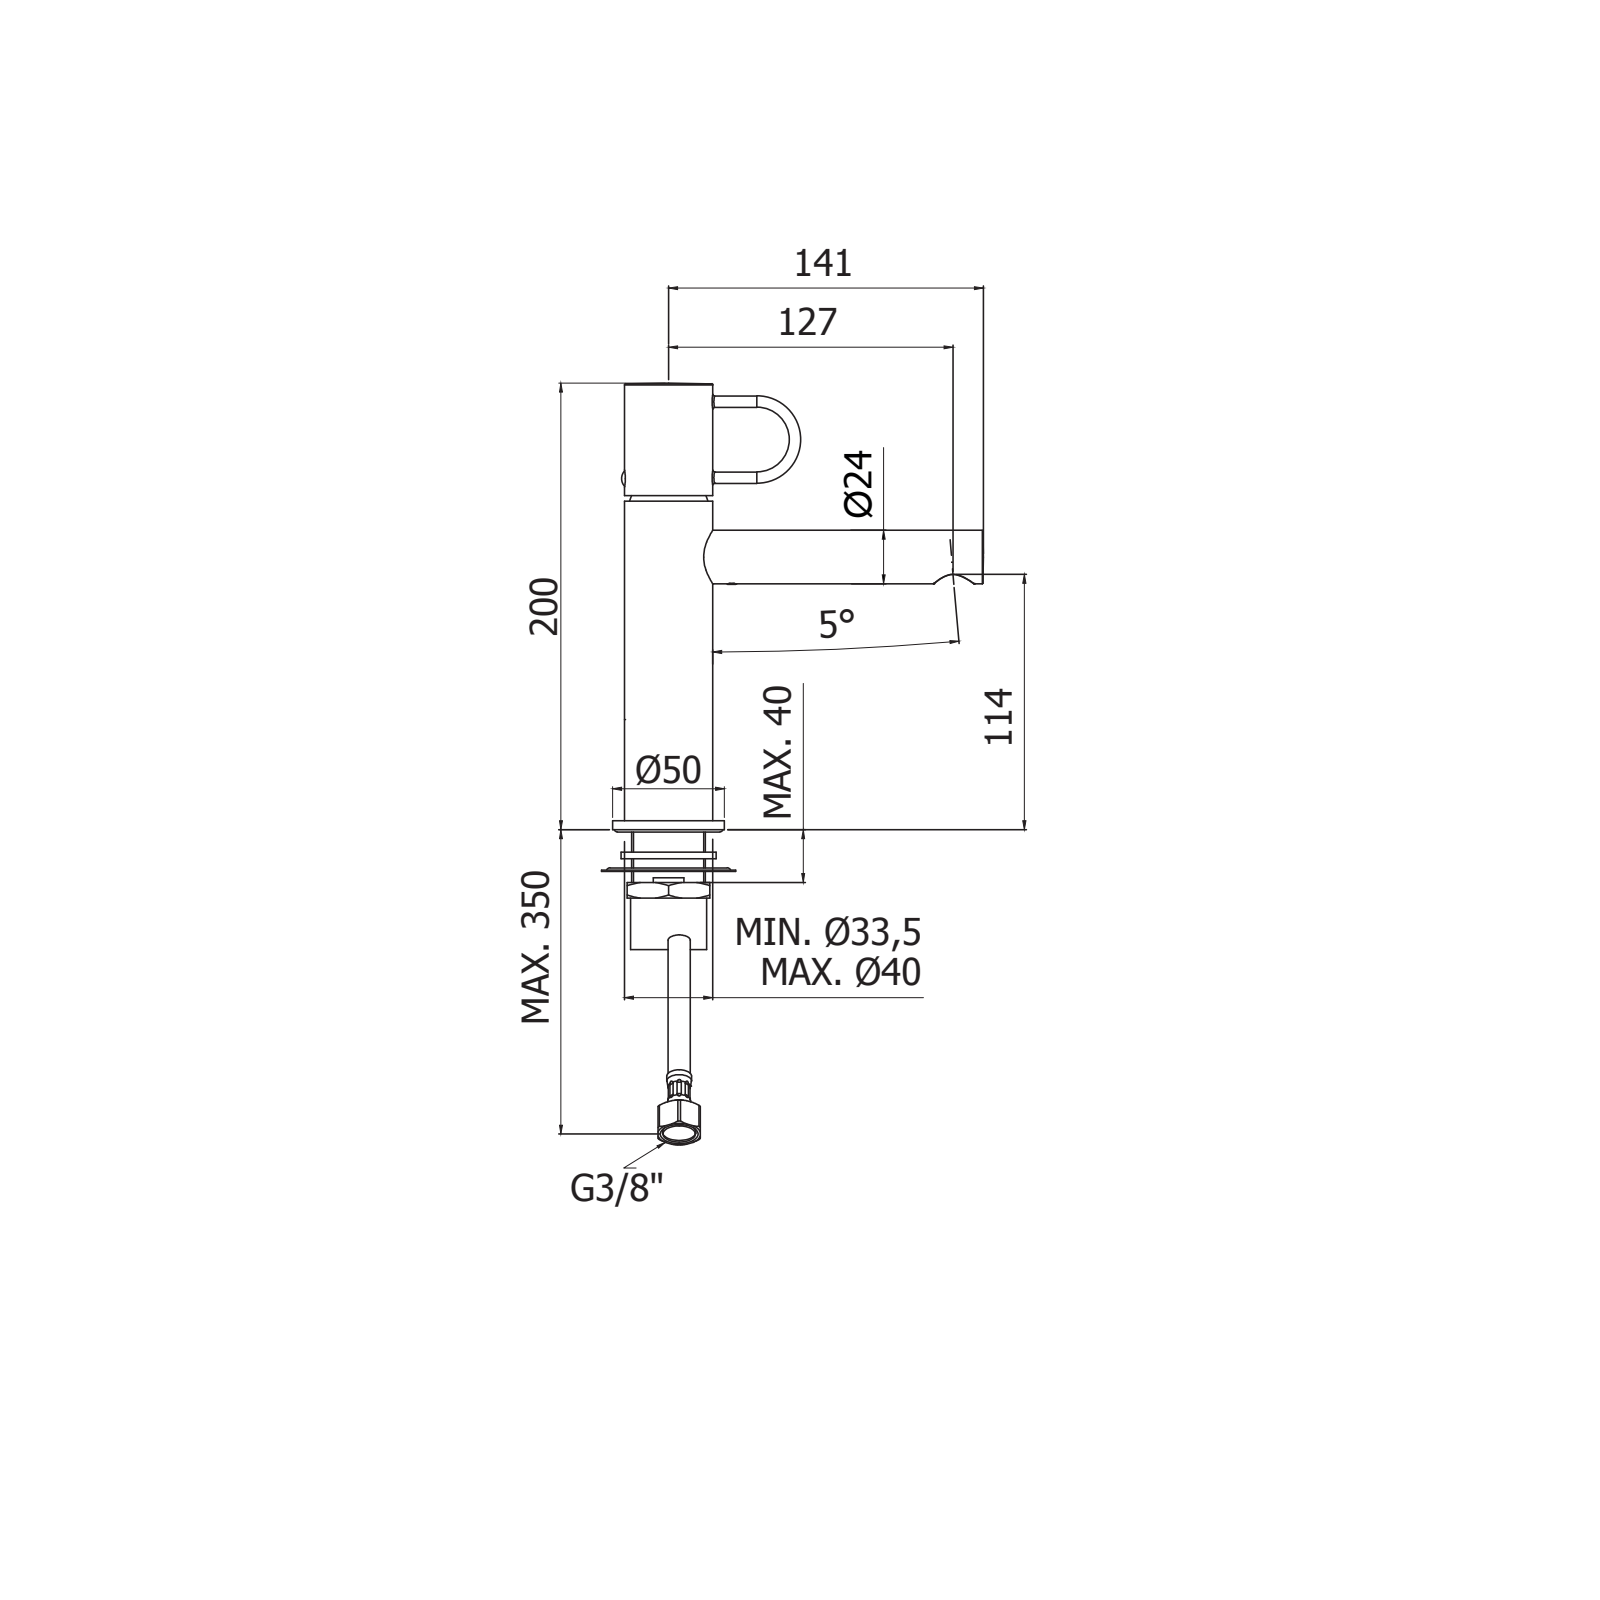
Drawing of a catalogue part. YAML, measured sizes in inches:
part_name: "JK071CR"
step_written_by: "CREO PARAMETRIC BY PTC INC, 2020044 (CONFIG_CONTROL_DESIGN)"
units: inches
bodies: {solids: 3, faces: 2912, planar: 1931, cylindrical: 615, other: 366}
overall_size: [7.868, 6.531, 1.969]
volume: 9.207
surface_area: 147.6
round_holes:
  - {diameter: 0.276, count: 3}
  - {diameter: 0.126, count: 2}
  - {diameter: 0.197, count: 2}
  - {diameter: 0.256, count: 2}
  - {diameter: 0.37, count: 2}
  - {diameter: 0.433, count: 2}
  - {diameter: 0.118, count: 1}
  - {diameter: 0.165, count: 1}
  - {diameter: 0.217, count: 1}
  - {diameter: 0.315, count: 1}
  - {diameter: 0.478, count: 1}
  - {diameter: 0.49, count: 1}
round_bosses_or_shafts:
  - {diameter: 0.035, count: 3}
  - {diameter: 0.433, count: 2}
  - {diameter: 0.394, count: 2}
  - {diameter: 0.354, count: 2}
  - {diameter: 0.197, count: 2}
  - {diameter: 0.157, count: 2}
  - {diameter: 1.969, count: 1}
  - {diameter: 1.693, count: 1}
partial_cylinders:
  - {radius: 0.005, count: 51}
  - {radius: 0.118, count: 28}
  - {radius: 0.02, count: 18}
  - {radius: 0.008, count: 8}
  - {radius: 0.039, count: 5}
  - {radius: 0.024, count: 4}
  - {radius: 0.079, count: 4}
  - {radius: 0.138, count: 3}
face_to_face_distances: [0.079, 0.157, 7.776, 7.618, 1.988, 0.256, 3.799, 3.642, 3.976, 0.583]
hole_center_spacings: [0.059, 0.265, 0.309, 0.351, 0.352, 0.367, 0.433, 0.609]
